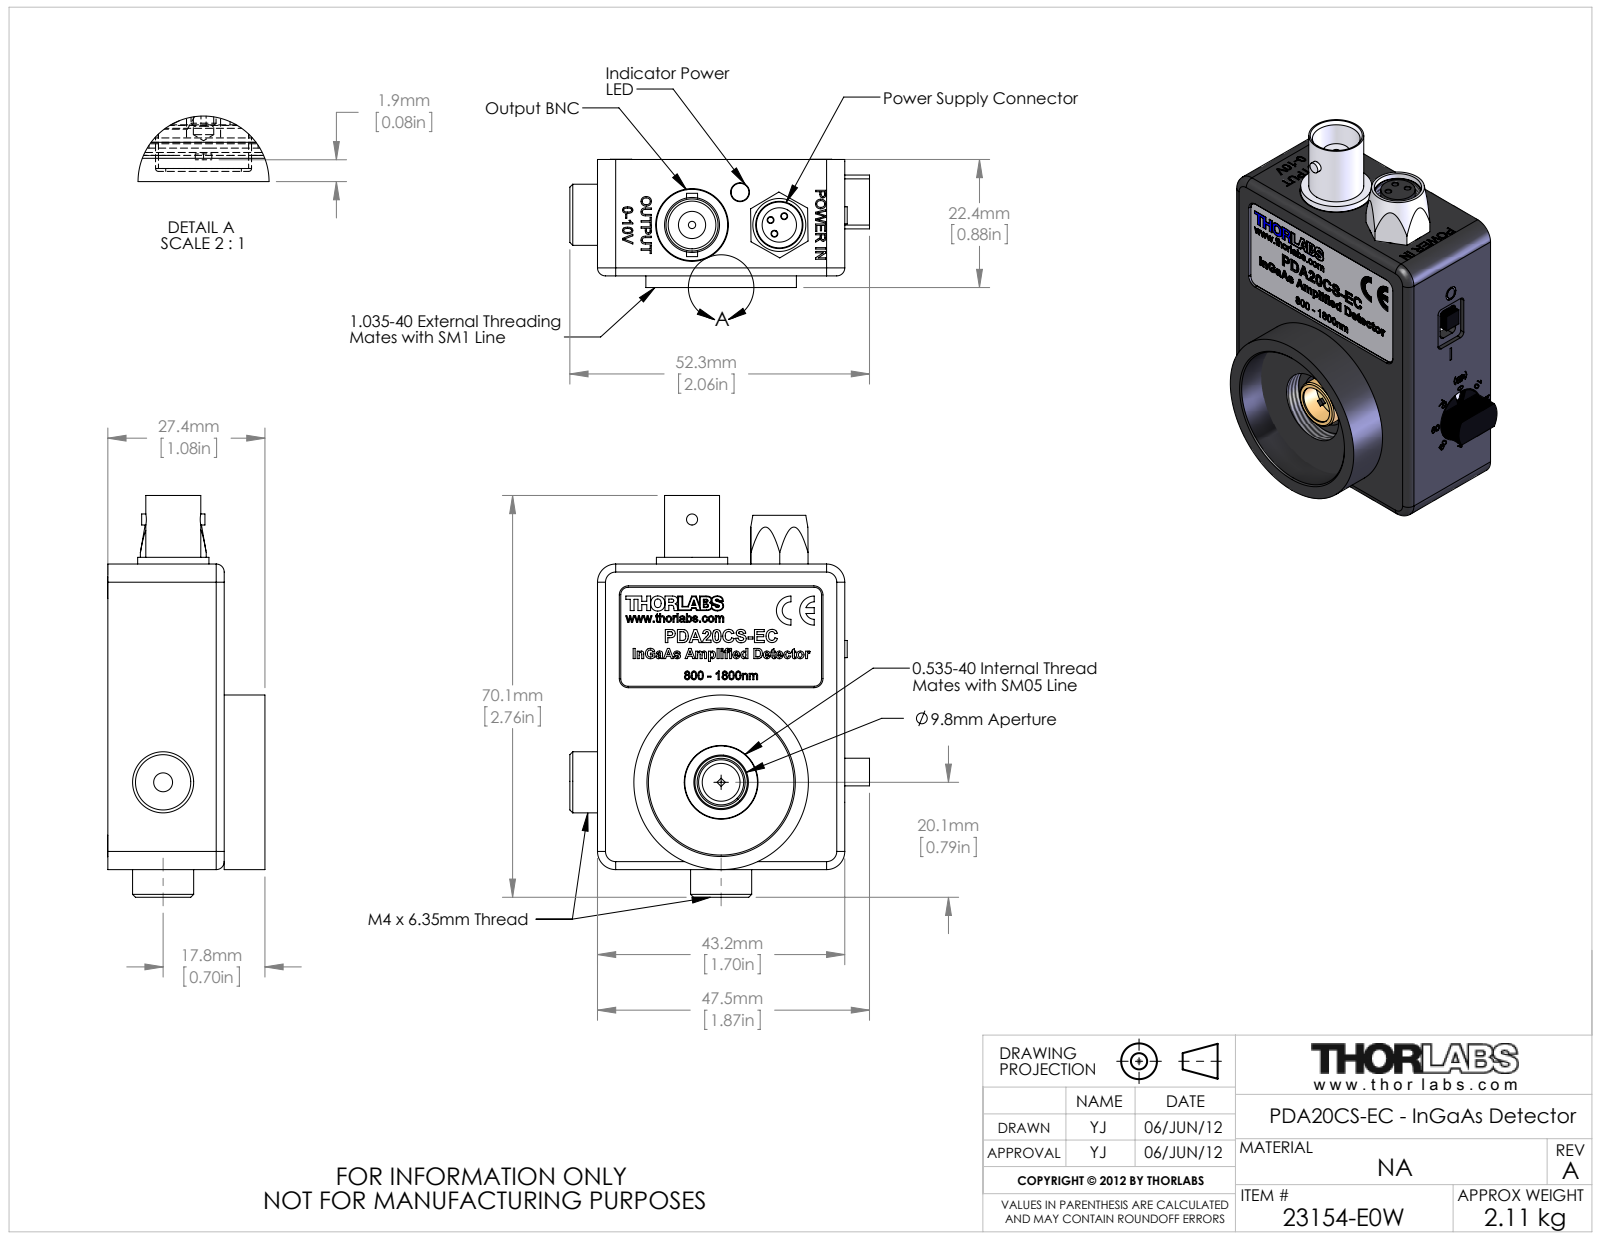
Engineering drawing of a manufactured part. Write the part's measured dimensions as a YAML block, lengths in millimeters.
part_name: "13053-001_Etching; 23155-002_PDA20CS-EC-LB1; 23154-E0W; SH2S019-1_HX-SHCS 0.086-56x0.188x0.188-N (+8 more)"
step_written_by: "SolidWorks 2011 (AUTOMOTIVE_DESIGN)"
units: millimeters
bodies: {solids: 24, faces: 2340, planar: 1177, cylindrical: 351, other: 812}
overall_size: [70.1, 52.3, 27.5]
volume: 25660
surface_area: 31540
round_holes:
  - {diameter: 0.9, count: 9}
  - {diameter: 0.8, count: 8}
  - {diameter: 1.8, count: 7}
  - {diameter: 2.4, count: 7}
  - {diameter: 0.8, count: 6}
  - {diameter: 3.2, count: 4}
  - {diameter: 5.1, count: 4}
  - {diameter: 0.7, count: 3}
  - {diameter: 0.8, count: 3}
  - {diameter: 1, count: 3}
  - {diameter: 1.3, count: 3}
  - {diameter: 3.3, count: 2}
round_bosses_or_shafts:
  - {diameter: 2.2, count: 7}
  - {diameter: 0.5, count: 6}
  - {diameter: 3.7, count: 4}
  - {diameter: 3.6, count: 3}
  - {diameter: 0.5, count: 3}
  - {diameter: 10.7, count: 2}
  - {diameter: 9.4, count: 2}
  - {diameter: 6, count: 2}
partial_cylinders:
  - {radius: 3.2, count: 23}
  - {radius: 0.8, count: 14}
  - {radius: 2.4, count: 8}
  - {radius: 1.3, count: 4}
  - {radius: 1.4, count: 4}
  - {radius: 0.6, count: 3}
  - {radius: 1.6, count: 3}
  - {radius: 5.6, count: 3}
face_to_face_distances: [1.6, 12.8, 14.4, 2.5, 1.6, 12.8, 11.2, 1.8, 1.3, 0.4]
hole_center_spacings: [2.5, 3.6, 2.5, 11.1, 11, 2, 2.5, 3.2]
